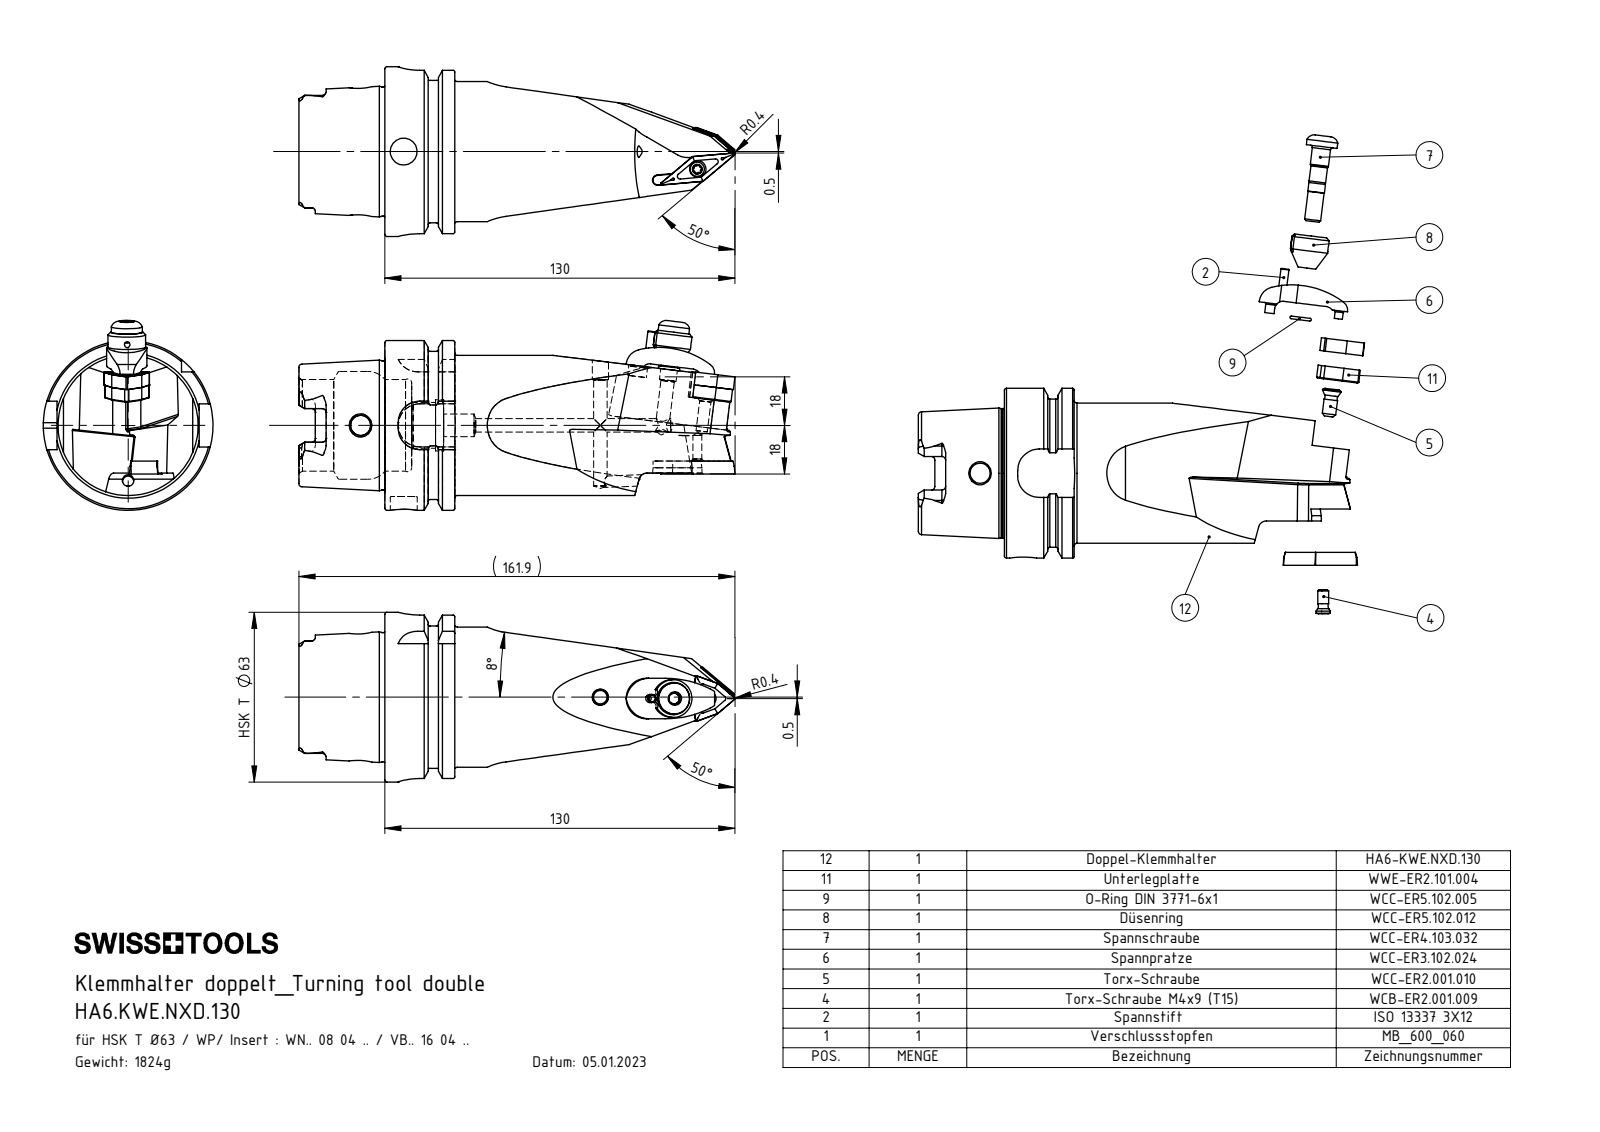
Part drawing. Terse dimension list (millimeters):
name: VBMT160404; WCC-ER5.102.005_A; WCC-ER5.102.012_B; ISO 13337 - 3 x 12_PreviewCfg (+8 more)
written by: SolidWorks 2017 (AUTOMOTIVE_DESIGN)
unit: mm
bodies: 13 solids, 627 faces (171 planar, 198 cylindrical, 258 other)
size: 161.9 × 70.45 × 63
volume: 231 352 mm³; area: 44 373 mm²
holes: 3× ⌀2, 3× ⌀5, 2× ⌀4.2, 2× ⌀7, 1× ⌀2.4, 1× ⌀3, 1× ⌀3.3, 1× ⌀4.4, 1× ⌀5.16, 1× ⌀6.1, 1× ⌀6.2, 1× ⌀6.7
bosses: 2× ⌀6, 2× ⌀4, 2× ⌀3, 1× ⌀63, 1× ⌀54.95, 1× ⌀52, 1× ⌀47.94, 1× ⌀14
rounds: 6× R0.34, 6× R0.39, 6× R0.59, 6× R1.4, 4× R0.5, 4× R2.88, 4× R8, 3× R0.4
face distances: 25.95, 16, 9.95, 4.76, 31.9, 41.85, 57.85, 52.8, 21.8, 4.47
hole spacings: 8, 8.01, 8.2, 14.8, 22.8, 23, 14.6, 14.79
